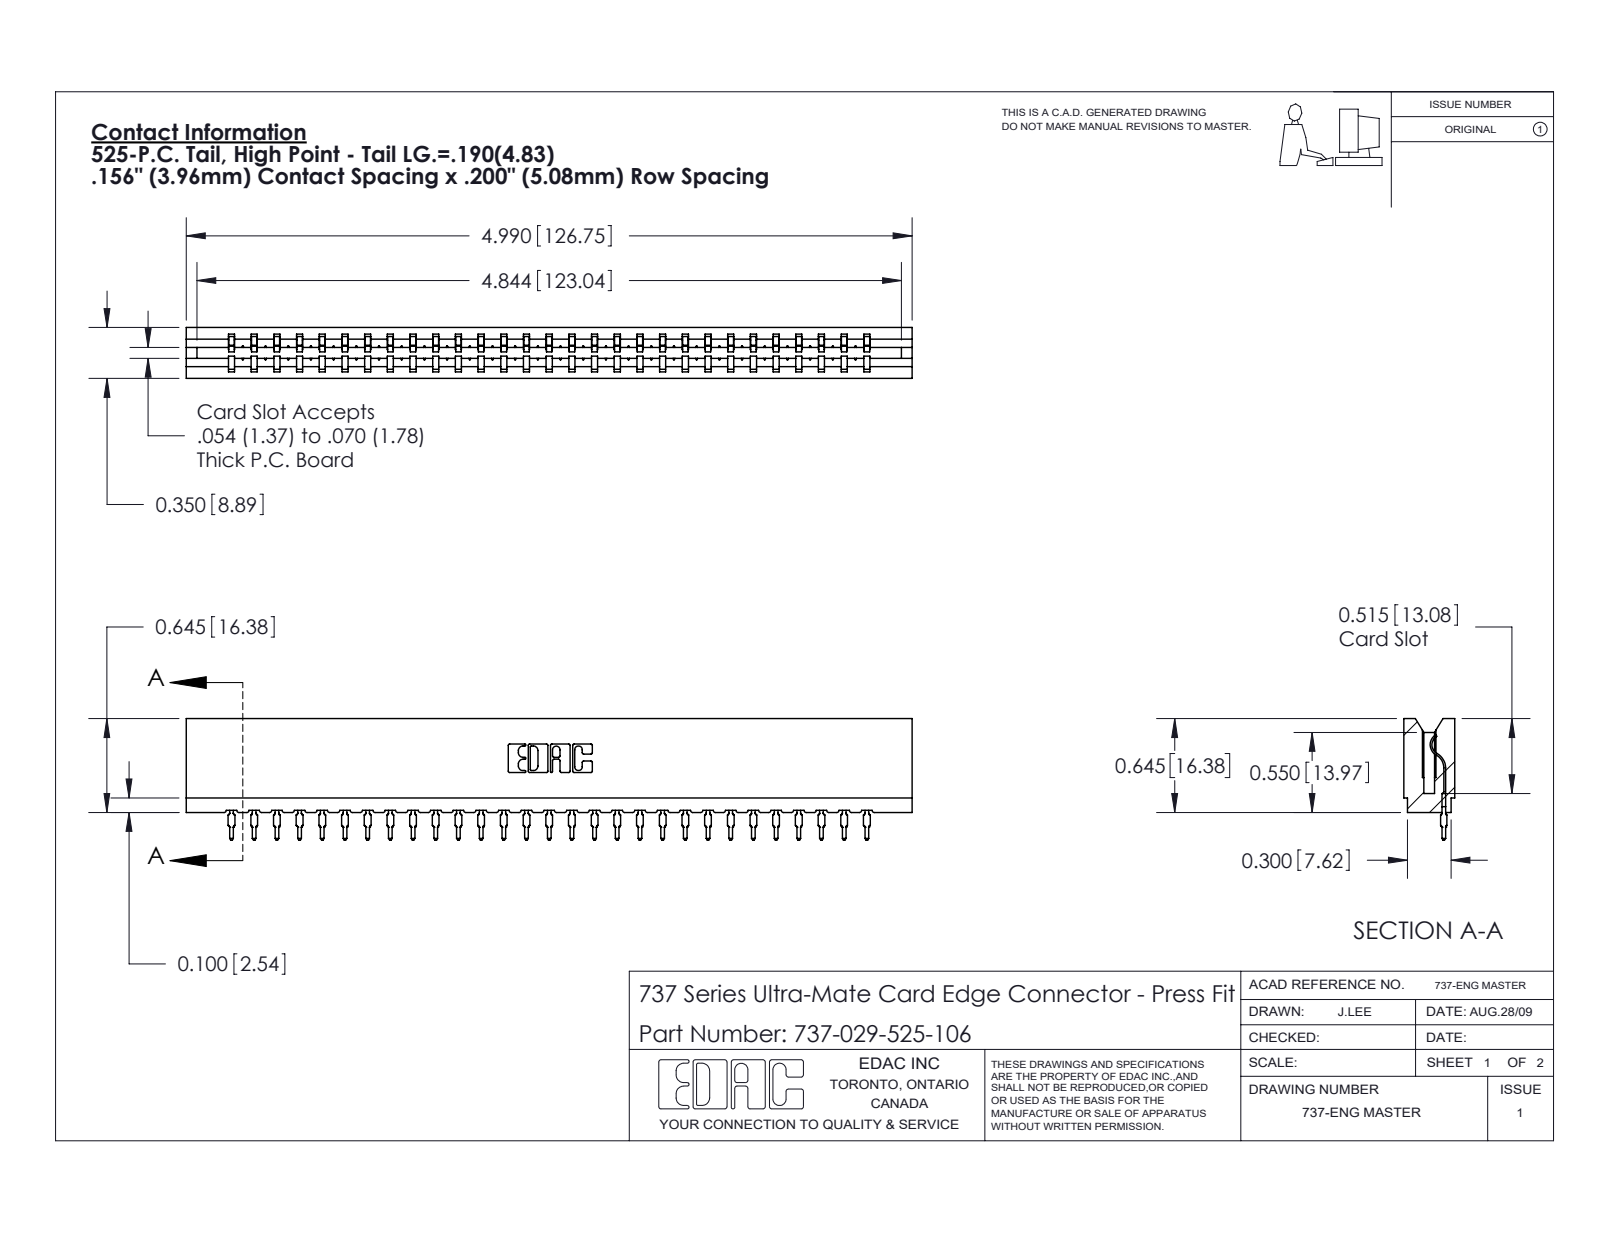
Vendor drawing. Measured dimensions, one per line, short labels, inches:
name: 737 Part_Insulator Option - 06; 737-029-525-106; 745-292-001_525
written by: SolidWorks 2020 (CONFIG_CONTROL_DESIGN)
unit: in
bodies: 30 solids, 3372 faces (2027 planar, 591 cylindrical, 754 other)
size: 4.99 × 0.836 × 0.35
volume: 0.75 in³; area: 25.13 in²
rounds: 58× R0.015, 58× R0.021, 22× R0.01, 6× R0.007, 6× R0.031, 4× R0.005, 4× R0.011, 3× R0.026
face distances: 0.138, 0.212, 0.35, 0.074, 0.156, 0.624, 0.045, 0.305, 0.093, 0.167
